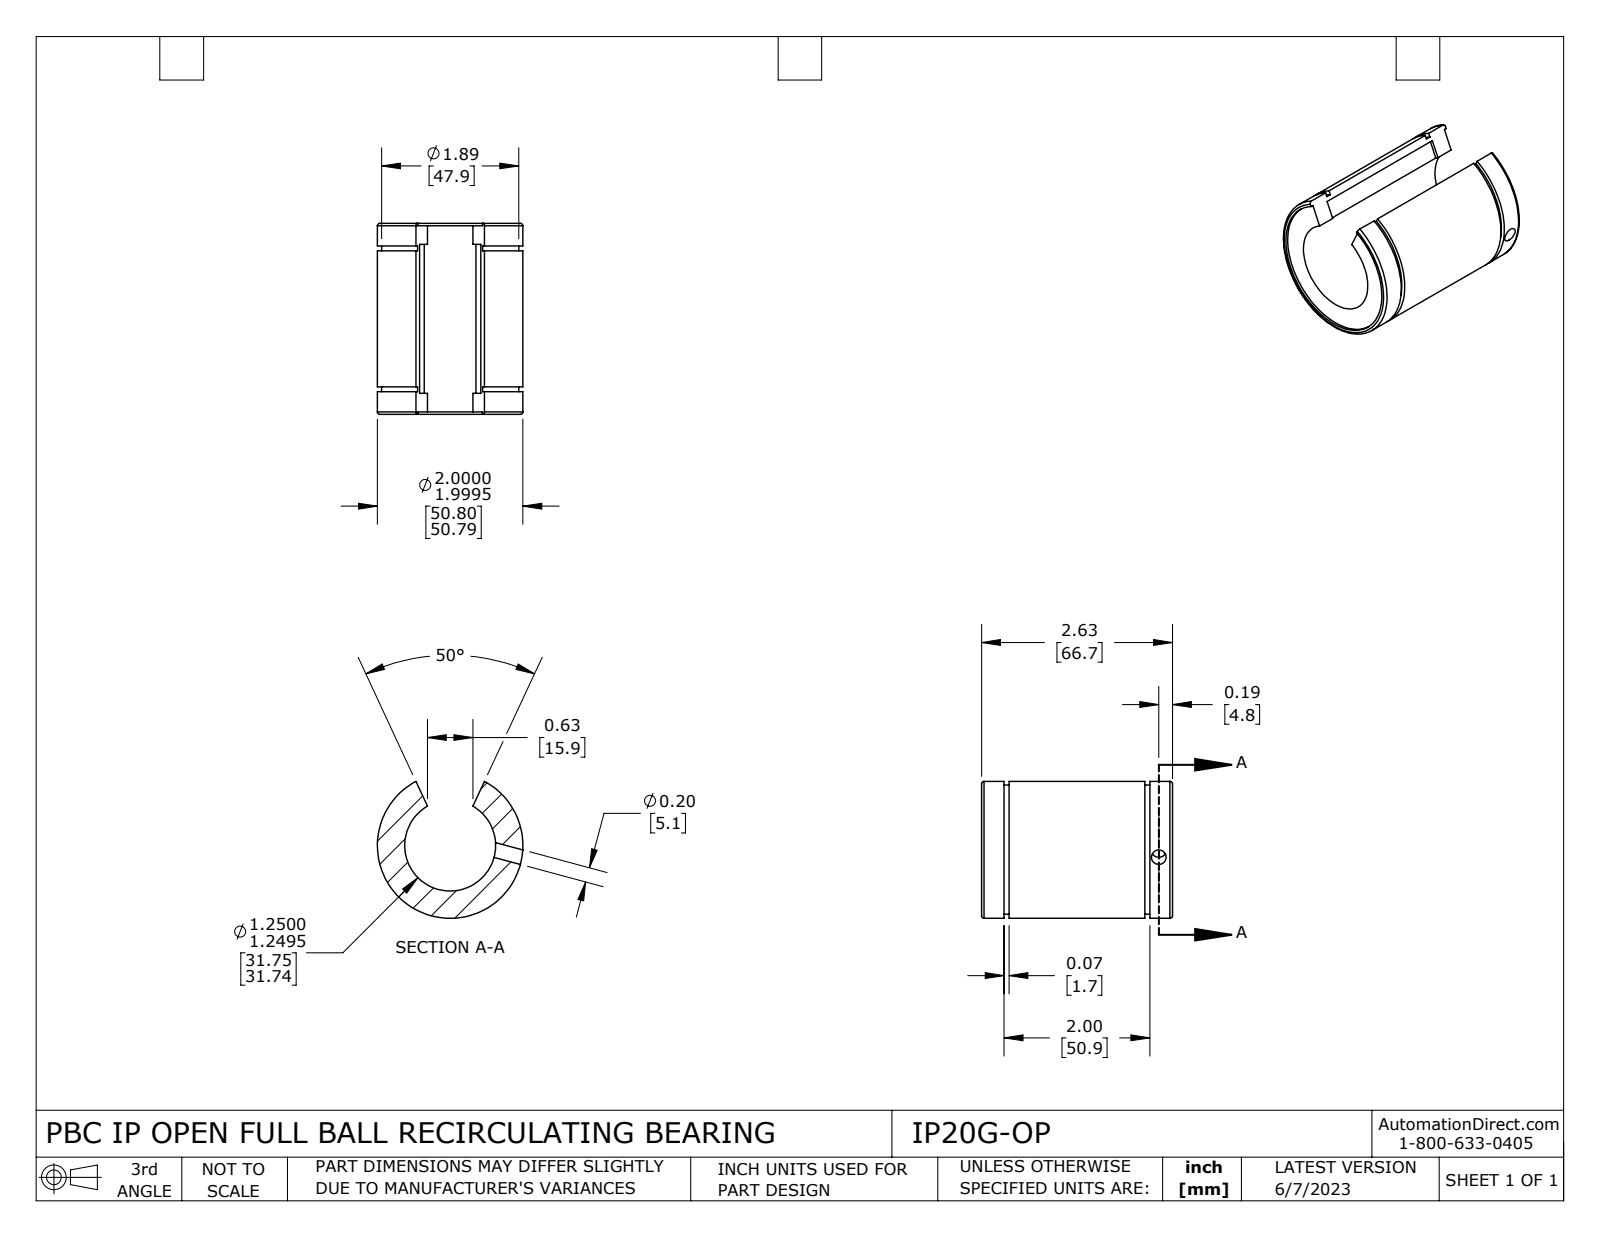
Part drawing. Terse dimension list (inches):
name: IP20G-OP
written by: SolidWorks 2021 (CONFIG_CONTROL_DESIGN)
unit: in
bodies: 1 solid, 40 faces (16 planar, 20 cylindrical, 4 other)
size: 2.625 × 2 × 1.882
volume: 4.028 in³; area: 28.96 in²
holes: 1× ⌀0.201, 1× ⌀1.25, 1× ⌀1.864
bosses: 1× ⌀2, 1× ⌀1.886
rounds: 1× R0.879
face distances: 2.557, 0.344, 2.213, 0.276, 2.281, 1.937, 0.068, 0.05, 0.05, 0.034
